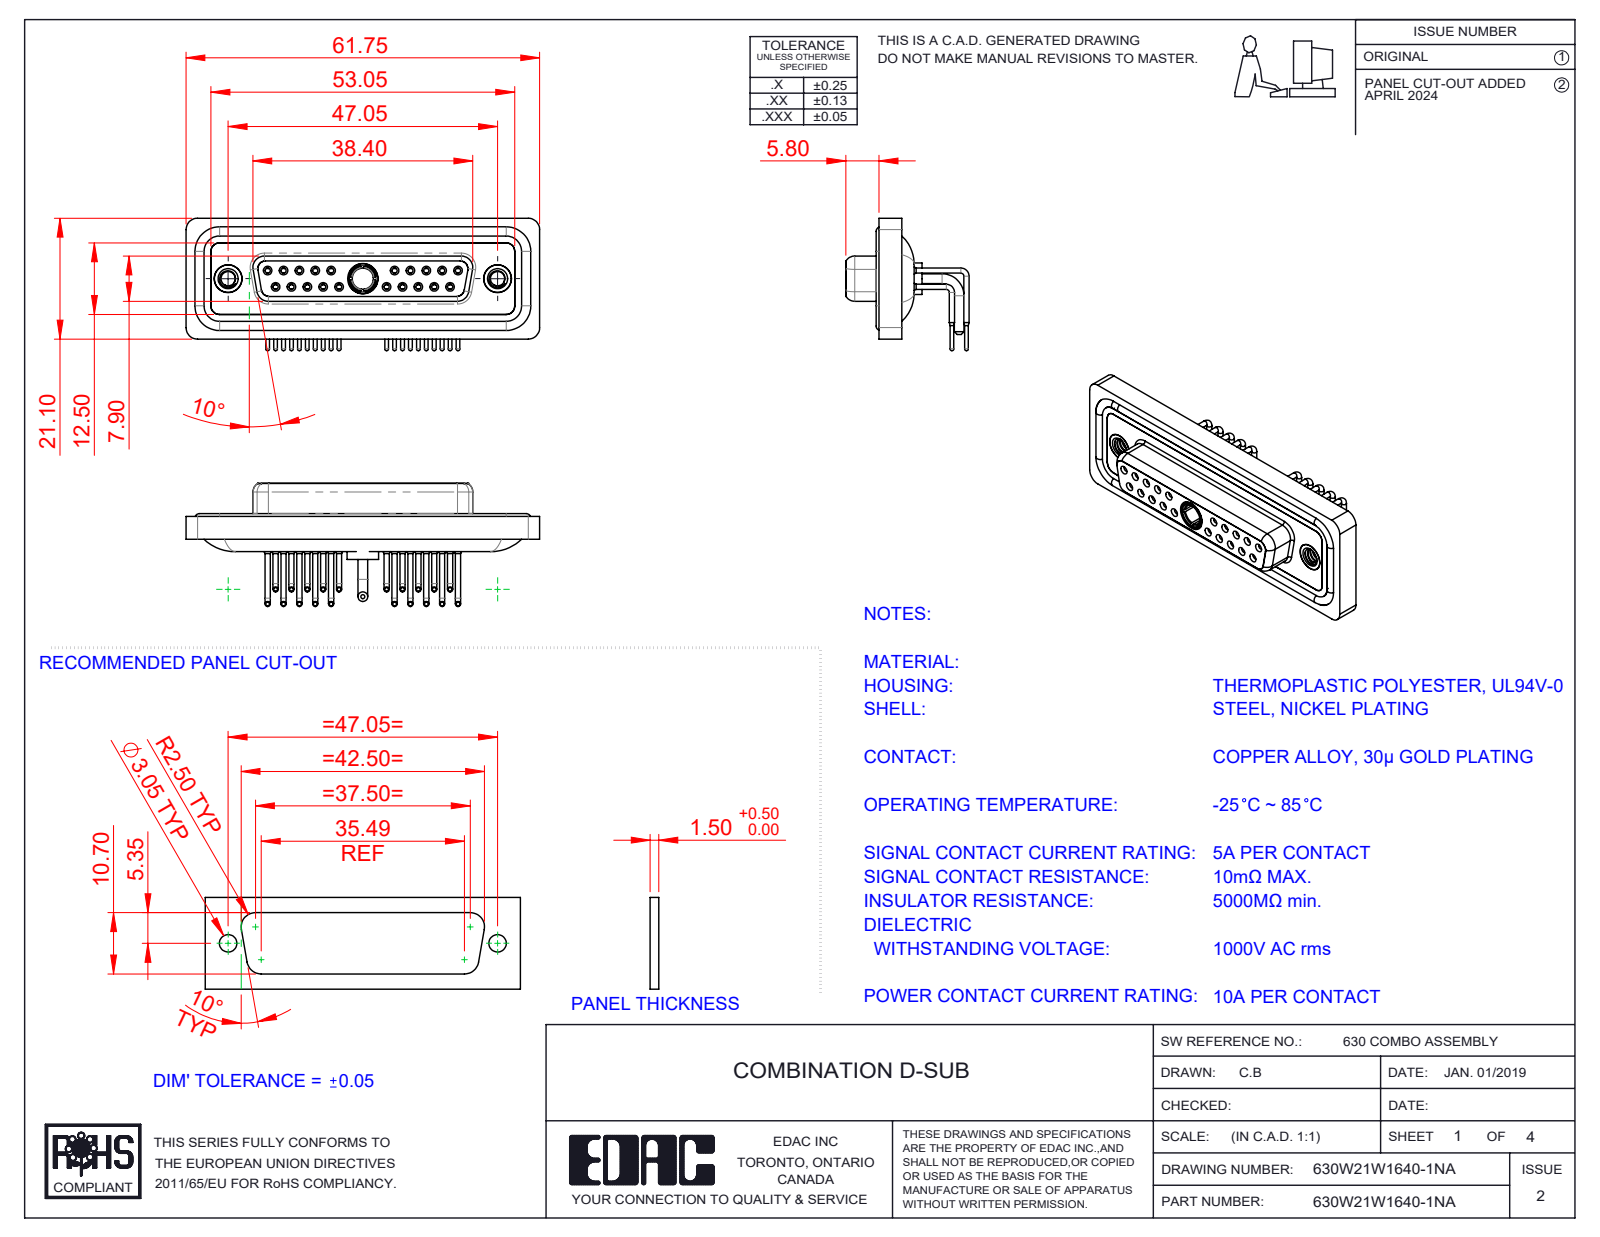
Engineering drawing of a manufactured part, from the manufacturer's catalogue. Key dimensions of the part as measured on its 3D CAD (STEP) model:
Part name (STEP PRODUCT): 630Combo Threaded Rivet_A; 630Combo Shell Front_25 Contacts; 630Combo Housing_21W1; 630Combo Contact Row 1_50 Contacts (+5 more)
STEP written by: SolidWorks 2023 (CONFIG_CONTROL_DESIGN)
Units: millimetres
Bodies: 29 solids, 1518 faces (434 planar, 671 cylindrical, 413 other)
Overall size (bounding box): 61.75 × 23.12 × 21.53
Volume: 8 440 mm³ · Surface area: 14 732 mm²
Round holes (diameter × count): ⌀0.9 ×20, ⌀1.1 ×20, ⌀1.5 ×20, ⌀2 ×20, ⌀1.6 ×10, ⌀1.7 ×10, ⌀4.85 ×3, ⌀2.5 ×2, ⌀4 ×2, ⌀4.05 ×2, ⌀5 ×2, ⌀3.7 ×1
Round bosses / shafts (diameter × count): ⌀0.9 ×20, ⌀0.65 ×20, ⌀1.6 ×14, ⌀4.95 ×2, ⌀4.8 ×2, ⌀1.7 ×2, ⌀5.5 ×1, ⌀5.2 ×1
Partial cylindrical surfaces — rounded edges, fillets, slot ends (radius × count): R1.5 ×18, R2 ×18, R1.35 ×8, R1.6 ×8, R0.25 ×4, R0.5 ×4, R0.6 ×4, R0.65 ×4
Main face-to-face distances: 0.4, 1.8, 4.1, 1.6, 1.1, 2.5, 1.5, 3.1, 9.8, 0.45
Hole centre spacings: 3.16, 2.77, 5.54, 8.31, 5.04, 19.39, 20.97, 22.16
